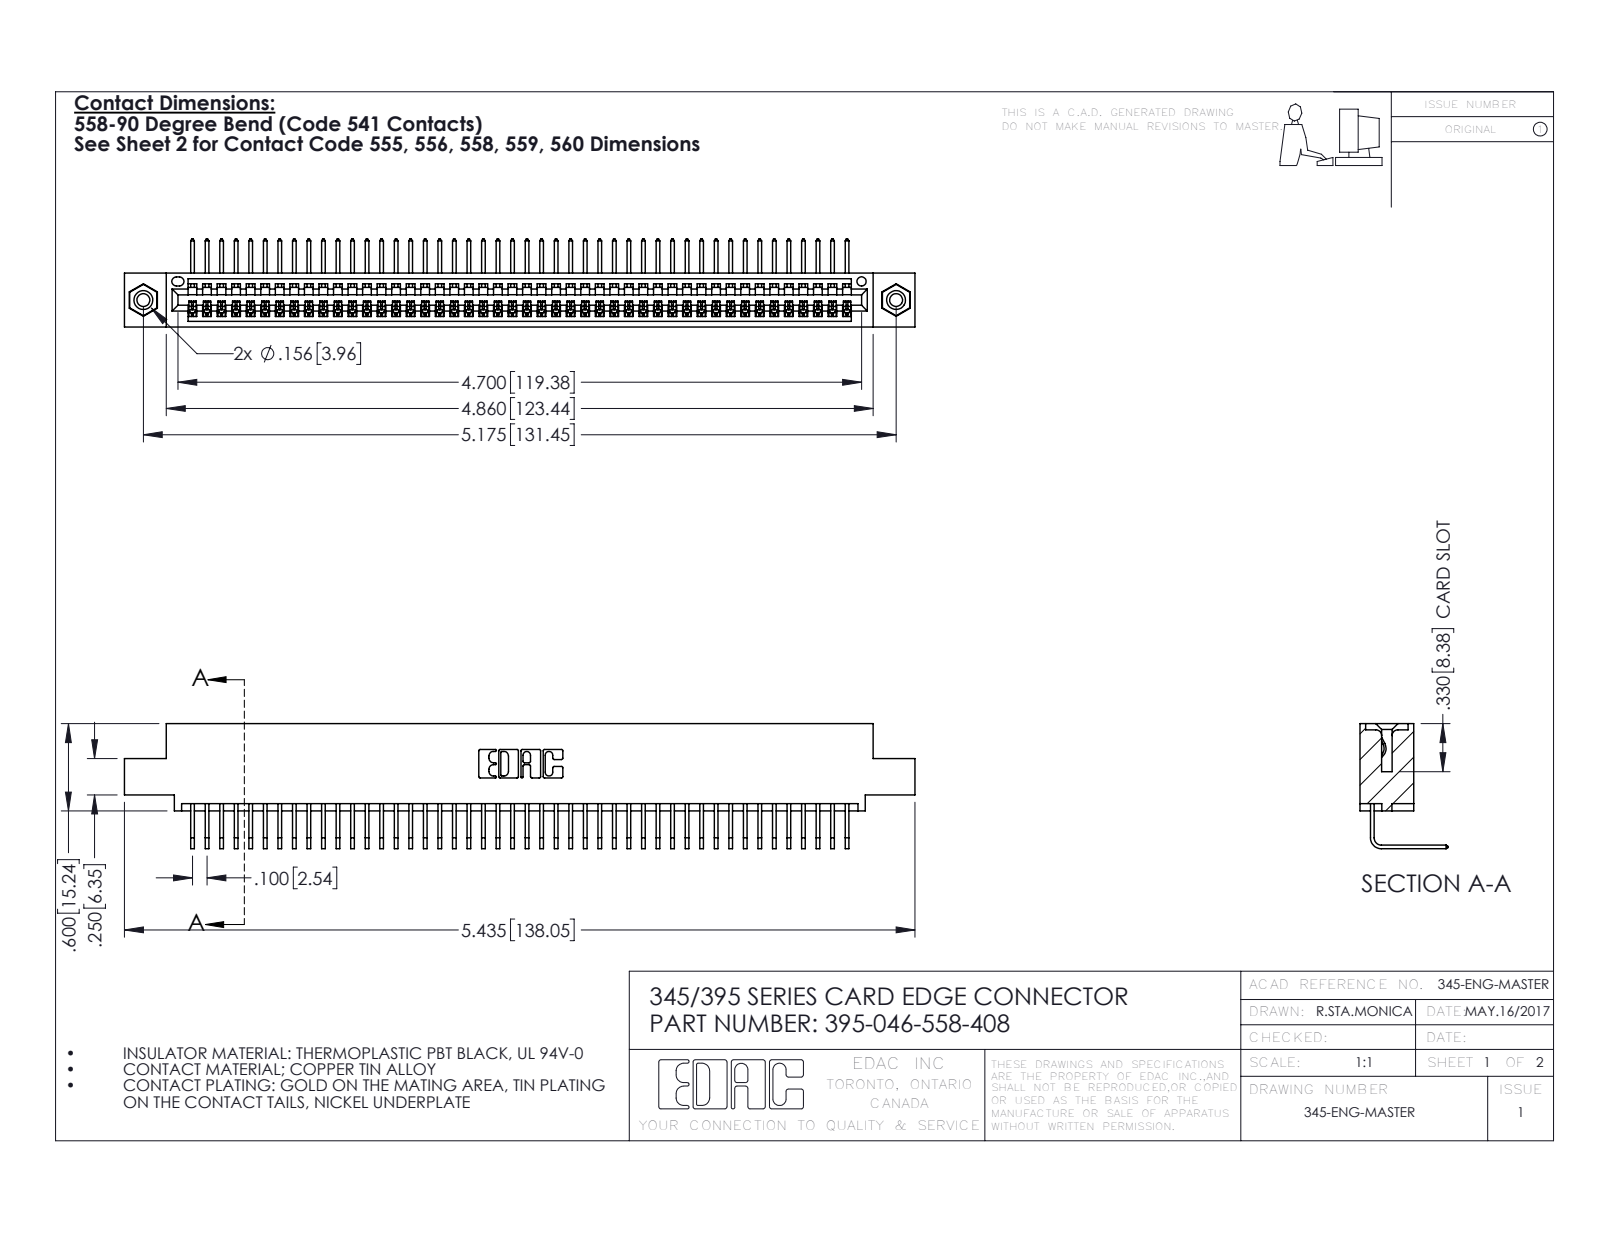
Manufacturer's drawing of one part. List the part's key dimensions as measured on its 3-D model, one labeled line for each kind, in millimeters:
Part name (STEP PRODUCT): 345 Part_0.110 Offset - 0.156 Dia-TI; 395-046-558-408; 345-292-001_558 Tail - 2; 345-250-001_345-250-003-102
STEP written by: SolidWorks 2016 (CONFIG_CONTROL_DESIGN)
Units: millimetres
Bodies: 49 solids, 2950 faces (2048 planar, 886 cylindrical, 16 other)
Overall size (bounding box): 138 × 21.8 × 15.4
Volume: 13 200 mm³ · Surface area: 18 620 mm²
Round holes (diameter × count): ⌀2.3 ×2, ⌀3.2 ×2, ⌀4 ×2, ⌀1.6 ×1
Round bosses / shafts (diameter × count): ⌀3.9 ×2
Partial cylindrical surfaces — rounded edges, fillets, slot ends (radius × count): R0.2 ×92, R0.3 ×22, R0.2 ×6, R0.8 ×6, R0.7 ×3, R0.8 ×2, R1 ×2, R0.4 ×1
Main face-to-face distances: 1.8, 7.6, 9.4, 5.1, 2.5, 6.9, 0.6, 5.7, 3.8, 1.8
Hole centre spacings: 6.9, 125.5, 131.4
